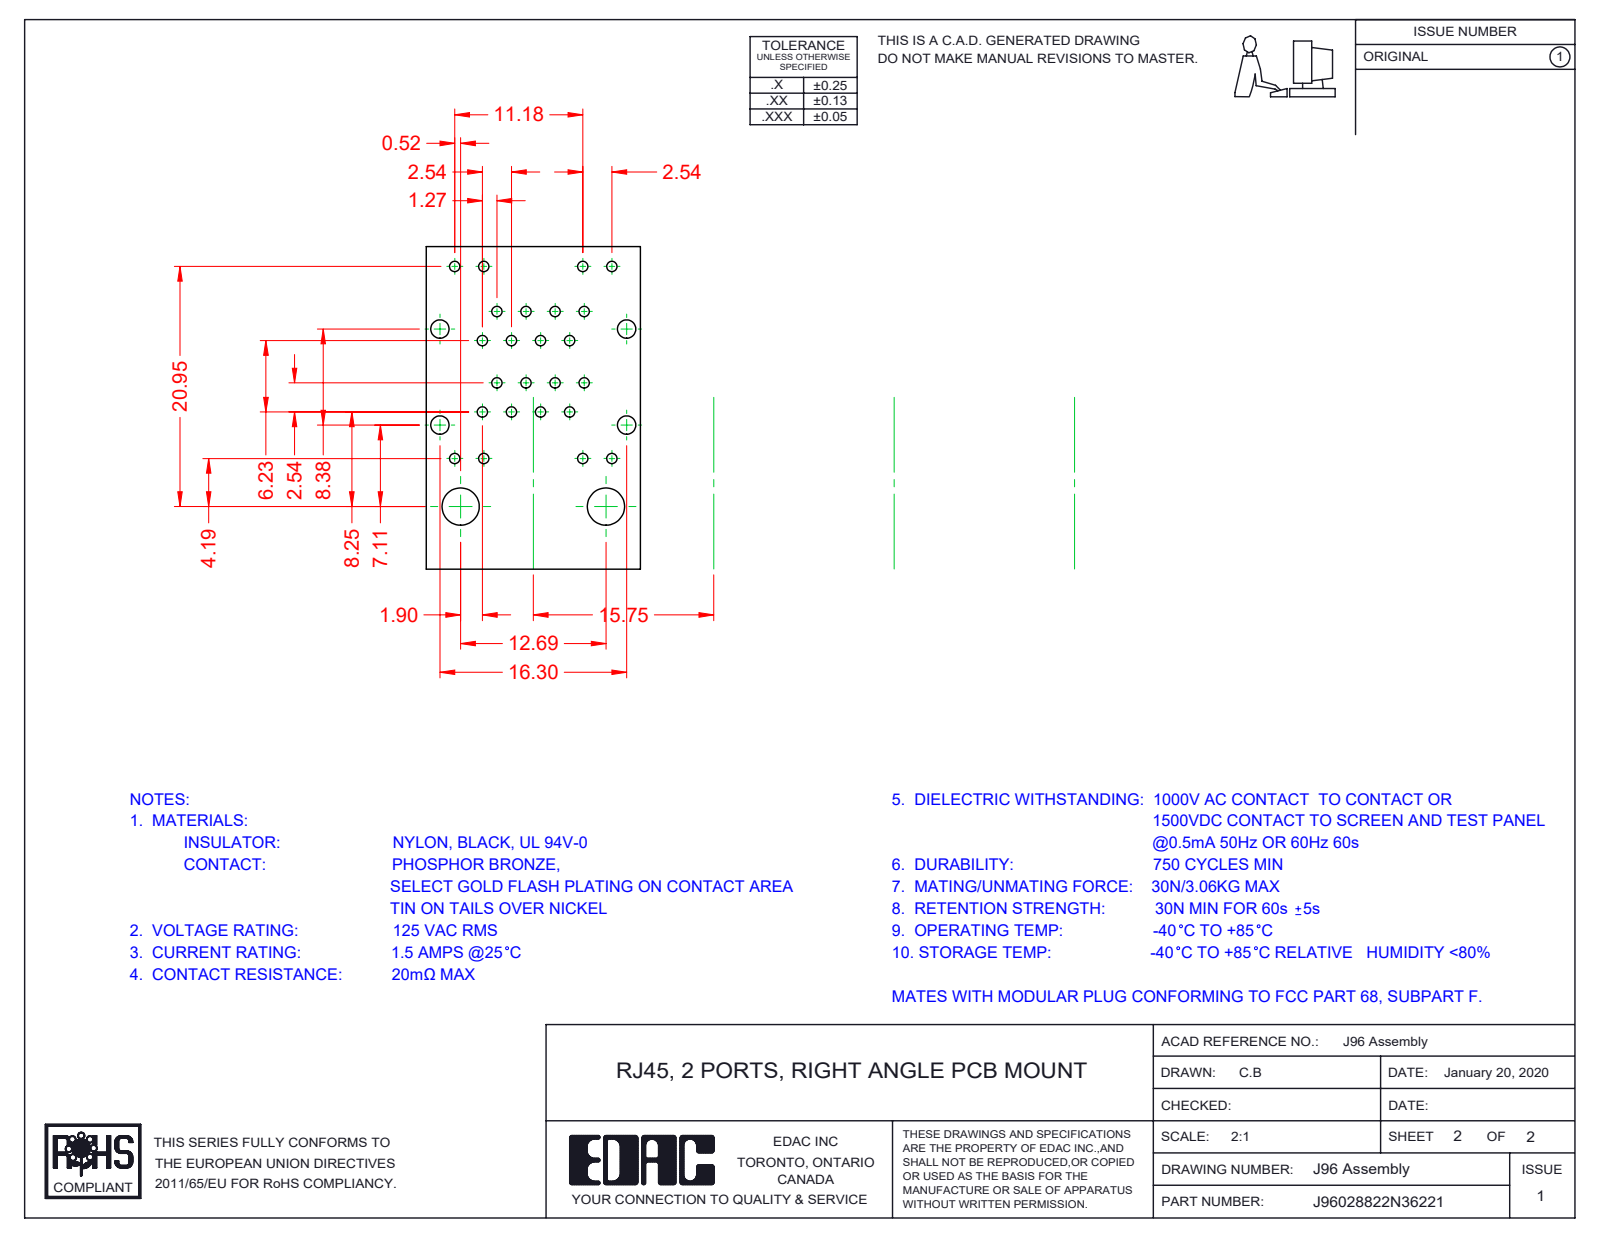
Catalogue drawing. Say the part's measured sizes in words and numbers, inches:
The part is named "96 Contact Lock Upper; 96 Back Plate_2 Ports; 96 LED RH Upper_6-Red-Green; 96 Shield_2 Ports LED - EMI (+8 more)". Its 3-D file was written by "SolidWorks 2016 (CONFIG_CONTROL_DESIGN)". It is 27 solids with 2421 faces: 1865 planar, 450 cylindrical and 106 other. Overall it measures 1.235 by 1.129 by 0.661 inches. Its volume is 0.418 cubic inches and its surface area 29.6 square inches. Partial cylindrical surfaces (rounded edges, fillets, slot ends): 48 of radius 0.01, 32 of radius 0.006, 24 of radius 0.014, 16 of radius 0.02, 16 of radius 0.039, 14 of radius 0.008, 9 of radius 0.028, 5 of radius 0.079. The main face-to-face distances are 0.642, 0.634, 0.069, 0.65, 0.581, 0.061, 0.573, 0.021, 0.058, 0.441.
